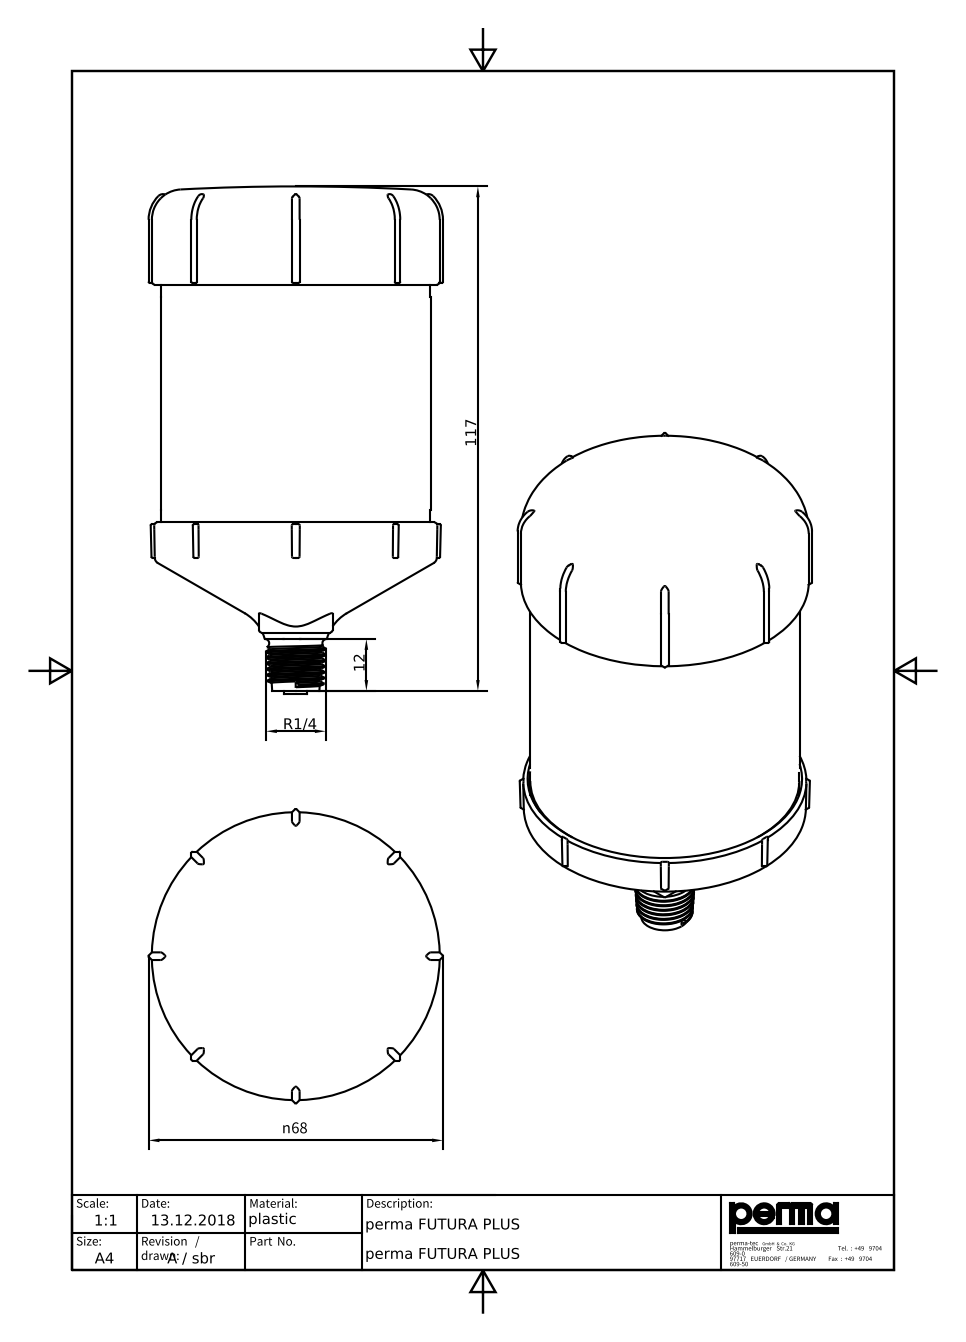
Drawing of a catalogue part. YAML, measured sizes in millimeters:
part_name: "perma FUTURA PLUS"
step_written_by: "Autodesk Inventor 2019 (AUTOMOTIVE_DESIGN)"
units: millimeters
bodies: {solids: 1, faces: 261, planar: 68, cylindrical: 82, other: 111}
overall_size: [117.35, 68, 68]
volume: 294909
surface_area: 25498
round_bosses_or_shafts:
  - {diameter: 66.5, count: 1}
  - {diameter: 62.15, count: 1}
  - {diameter: 5.4, count: 1}
partial_cylinders:
  - {radius: 0.3, count: 52}
  - {radius: 0.6, count: 8}
face_to_face_distances: [54.94, 15.63, 32.63, 48.26, 38.91, 93.85, 17, 13.5, 25.41, 80.35]
